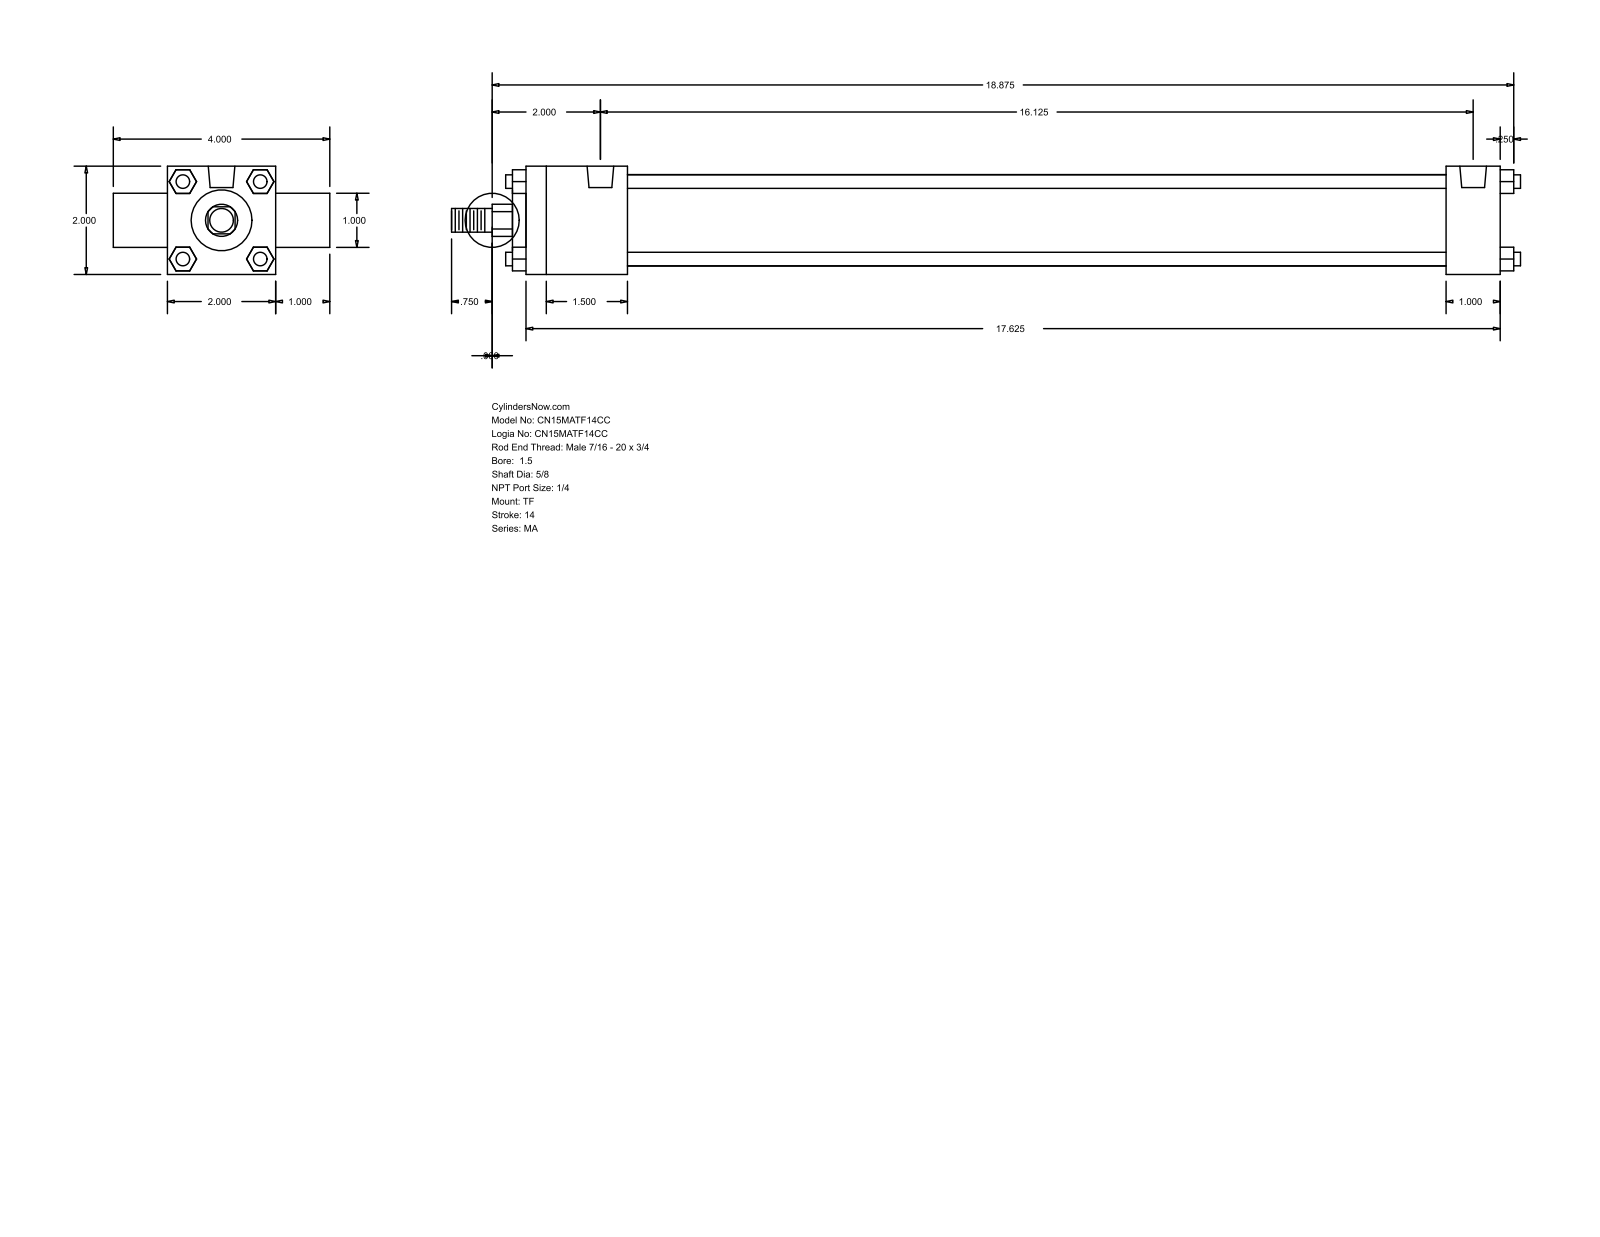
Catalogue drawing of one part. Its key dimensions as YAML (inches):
part_name: "MA_TF__0150_0.625"
step_written_by: "GSSL Pune (CONFIG_CONTROL_DESIGN)"
units: inches
bodies: {solids: 0, faces: 120, planar: 92, cylindrical: 28, other: 0}
overall_size: [19.75, 4, 2]
round_holes:
  - {diameter: 0.313, count: 3}
  - {diameter: 0.492, count: 2}
round_bosses_or_shafts:
  - {diameter: 0.25, count: 4}
  - {diameter: 1.69, count: 1}
  - {diameter: 1.125, count: 1}
  - {diameter: 1, count: 1}
  - {diameter: 0.625, count: 1}
  - {diameter: 0.437, count: 1}
partial_cylinders:
  - {radius: 0.297, count: 1}
face_to_face_distances: [2, 18, 1, 3, 1.875, 17, 15.125, 16.125, 1, 0.25]
hole_center_spacings: [16.125]
